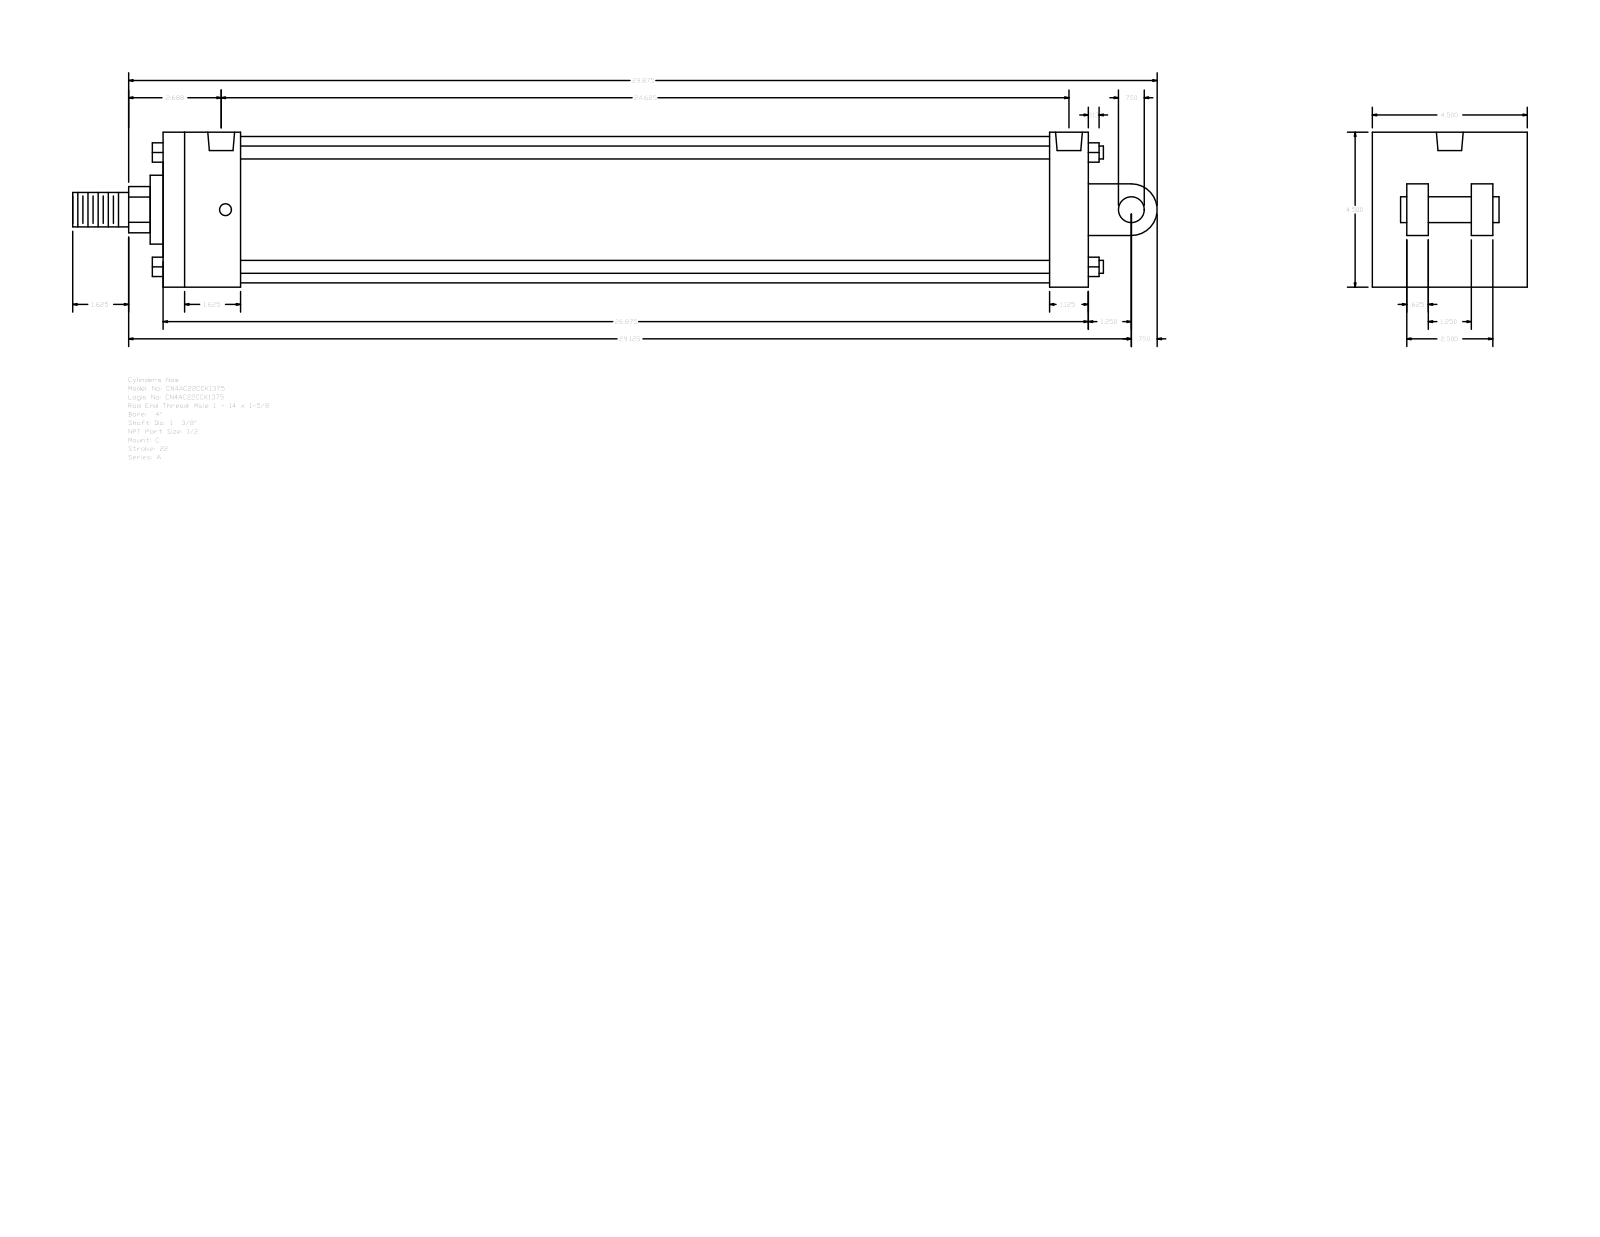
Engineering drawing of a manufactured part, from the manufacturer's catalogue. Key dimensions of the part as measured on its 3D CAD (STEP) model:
Part name (STEP PRODUCT): A_C__0400_1.375
STEP written by: GSSL Pune (CONFIG_CONTROL_DESIGN)
Units: millimetres
Bodies: 0 solids, 135 faces (102 planar, 33 cylindrical, 0 other)
Overall size (bounding box): 800.1 × 114.3 × 114.3
Round holes (diameter × count): ⌀8.73 ×4, ⌀19.77 ×2
Round bosses / shafts (diameter × count): ⌀9.53 ×4, ⌀107.95 ×1, ⌀50.8 ×1, ⌀34.92 ×1, ⌀25.4 ×1, ⌀19.05 ×1
Partial cylindrical surfaces — rounded edges, fillets, slot ends (radius × count): R17.06 ×1, R19.05 ×1
Main face-to-face distances: 114.3, 682.62, 57.15, 73.03, 654.05, 28.57, 596.9, 625.47, 41.27, 25.4
Hole centre spacings: 3.18, 619.12, 622.3, 625.48
